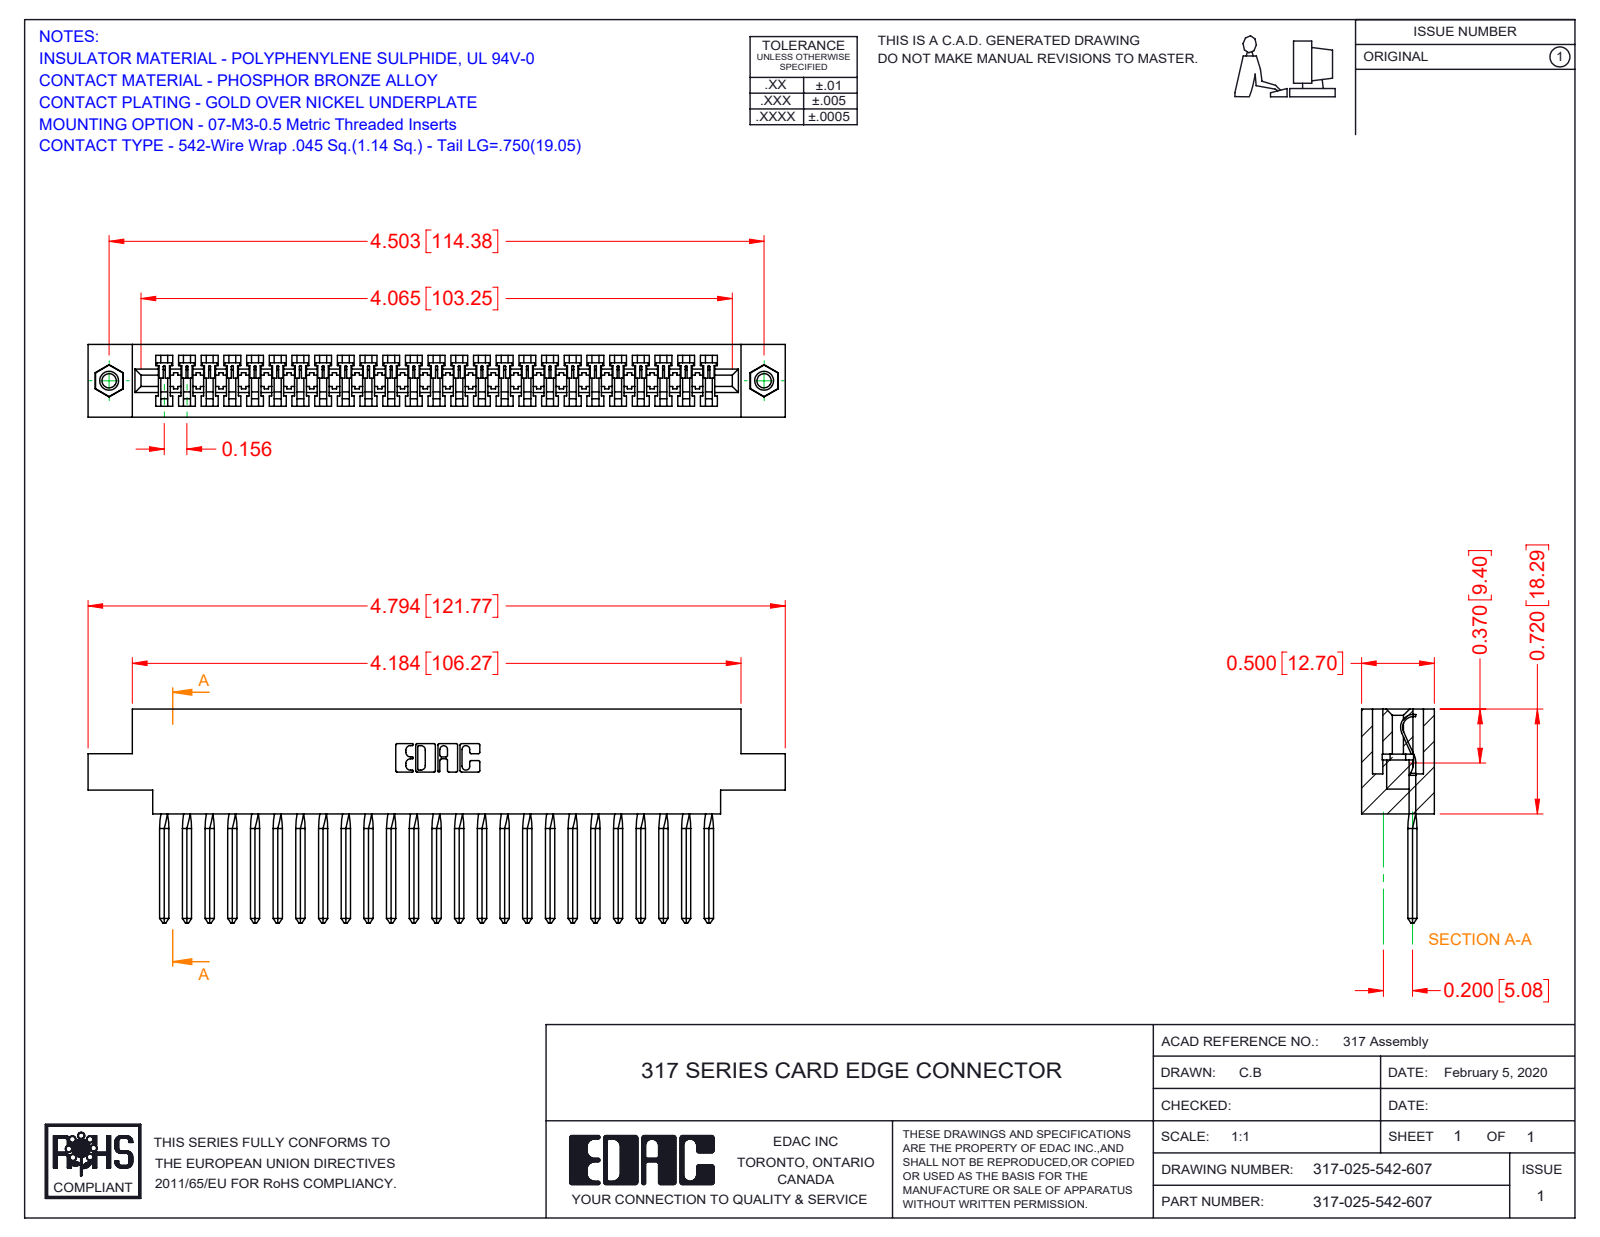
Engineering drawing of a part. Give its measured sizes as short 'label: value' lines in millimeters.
name: 317-025-542-607; 317 Part_.156 Dia - TI; 345-250-001_345-250-005-103; 317-290-003_542
written by: SolidWorks 2016 (CONFIG_CONTROL_DESIGN)
unit: mm
bodies: 28 solids, 2037 faces (1690 planar, 231 cylindrical, 116 other)
size: 121.8 × 37.3 × 12.7
volume: 18 340 mm³; area: 22 030 mm²
holes: 2× ⌀2.5, 2× ⌀3.2, 2× ⌀4
bosses: 2× ⌀3.9
rounds: 50× R0.2, 22× R0.3, 6× R0.2, 6× R0.8, 3× R0.7, 1× R1.9, 1× R2.3, 1× R2.5
face distances: 12.7, 1.9, 10.8, 8.9, 2.8, 3.5, 18.3, 5.4, 7.3, 5.4
hole spacings: 114.4
